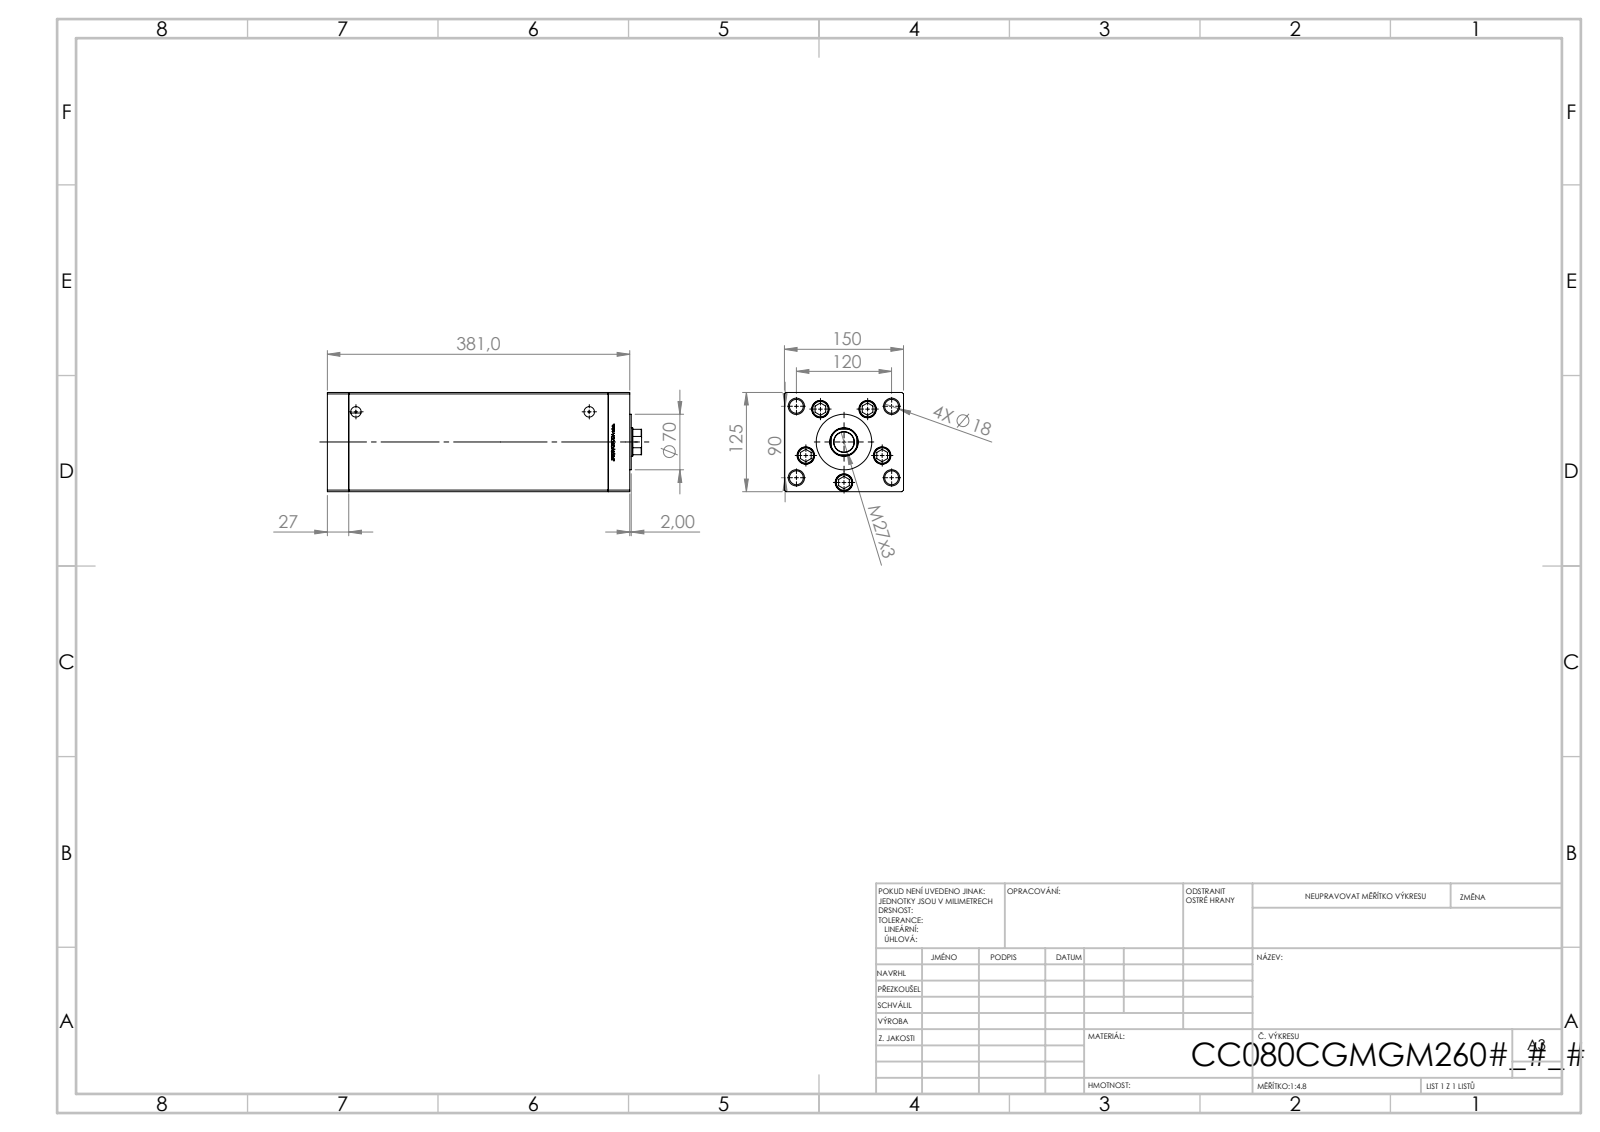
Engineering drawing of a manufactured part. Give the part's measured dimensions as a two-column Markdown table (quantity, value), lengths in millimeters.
| quantity | value |
| --- | --- |
| part name | ALLEN BOLT; V220C_C MIDDLE; V220C FRONT; V220C BACK_C (+1 more) |
| STEP written by | SolidWorks 2019 (CONFIG_CONTROL_DESIGN) |
| units | millimeters |
| bodies | 13 solids, 1175 faces (546 planar, 167 cylindrical, 462 other) |
| overall size | 396 × 150 × 125 |
| volume | 5 724 000 mm³ |
| surface area | 553 455 mm² |
| round holes (diameter × count) | 17.5 × 9, 22 × 5, 16 × 4, 20.5 × 4, 2 × 2, 13.16 × 2, 21 × 1, 25.5 × 1, 36 × 1 |
| round bosses / shafts (diameter × count) | 8 × 5, 21 × 4, 80 × 1, 70 × 1 |
| partial cylindrical surfaces (radius × count) | 0.93 × 2, 17.5 × 1 |
| main face-to-face distances | 125, 150, 27, 354, 327, 33.5, 6.5, 381, 347.5, 320.5 |
| hole center spacings | 51, 75, 30.43, 30.48, 58.89, 60.3, 61.25, 63.14 |
